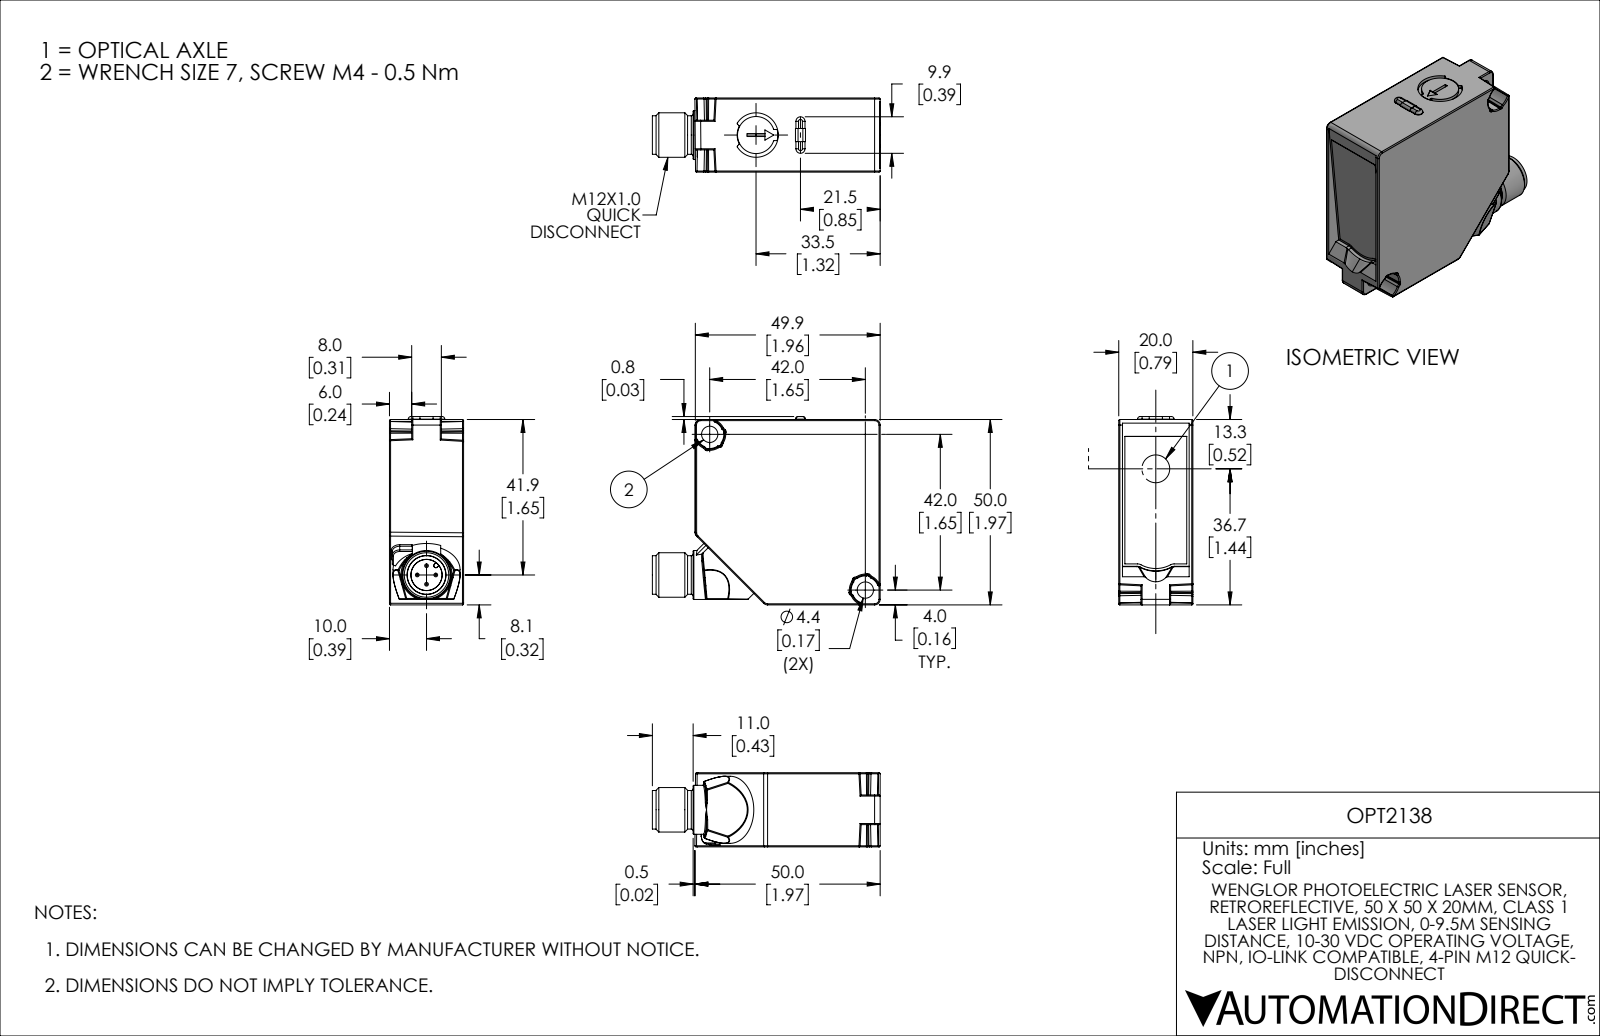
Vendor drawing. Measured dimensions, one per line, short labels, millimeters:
name: OPT2138
written by: SolidWorks 2019 (AUTOMOTIVE_DESIGN)
unit: mm
bodies: 3 solids, 347 faces (112 planar, 120 cylindrical, 115 other)
size: 72.5 × 50.8 × 20
volume: 46 150 mm³; area: 10 660 mm²
holes: 2× ⌀4.4, 1× ⌀12, 1× ⌀18.1
bosses: 4× ⌀1, 1× ⌀13.2, 1× ⌀12, 1× ⌀10.4, 1× ⌀10, 1× ⌀0.2
rounds: 63× R0.3, 8× R0.2, 5× R1.5, 5× R2, 4× R0.7, 2× R1.2, 1× R5.1, 1× R5.9
face distances: 20, 50, 1, 19, 6, 14, 5, 13, 1.5, 48.5
hole spacings: 59.4
